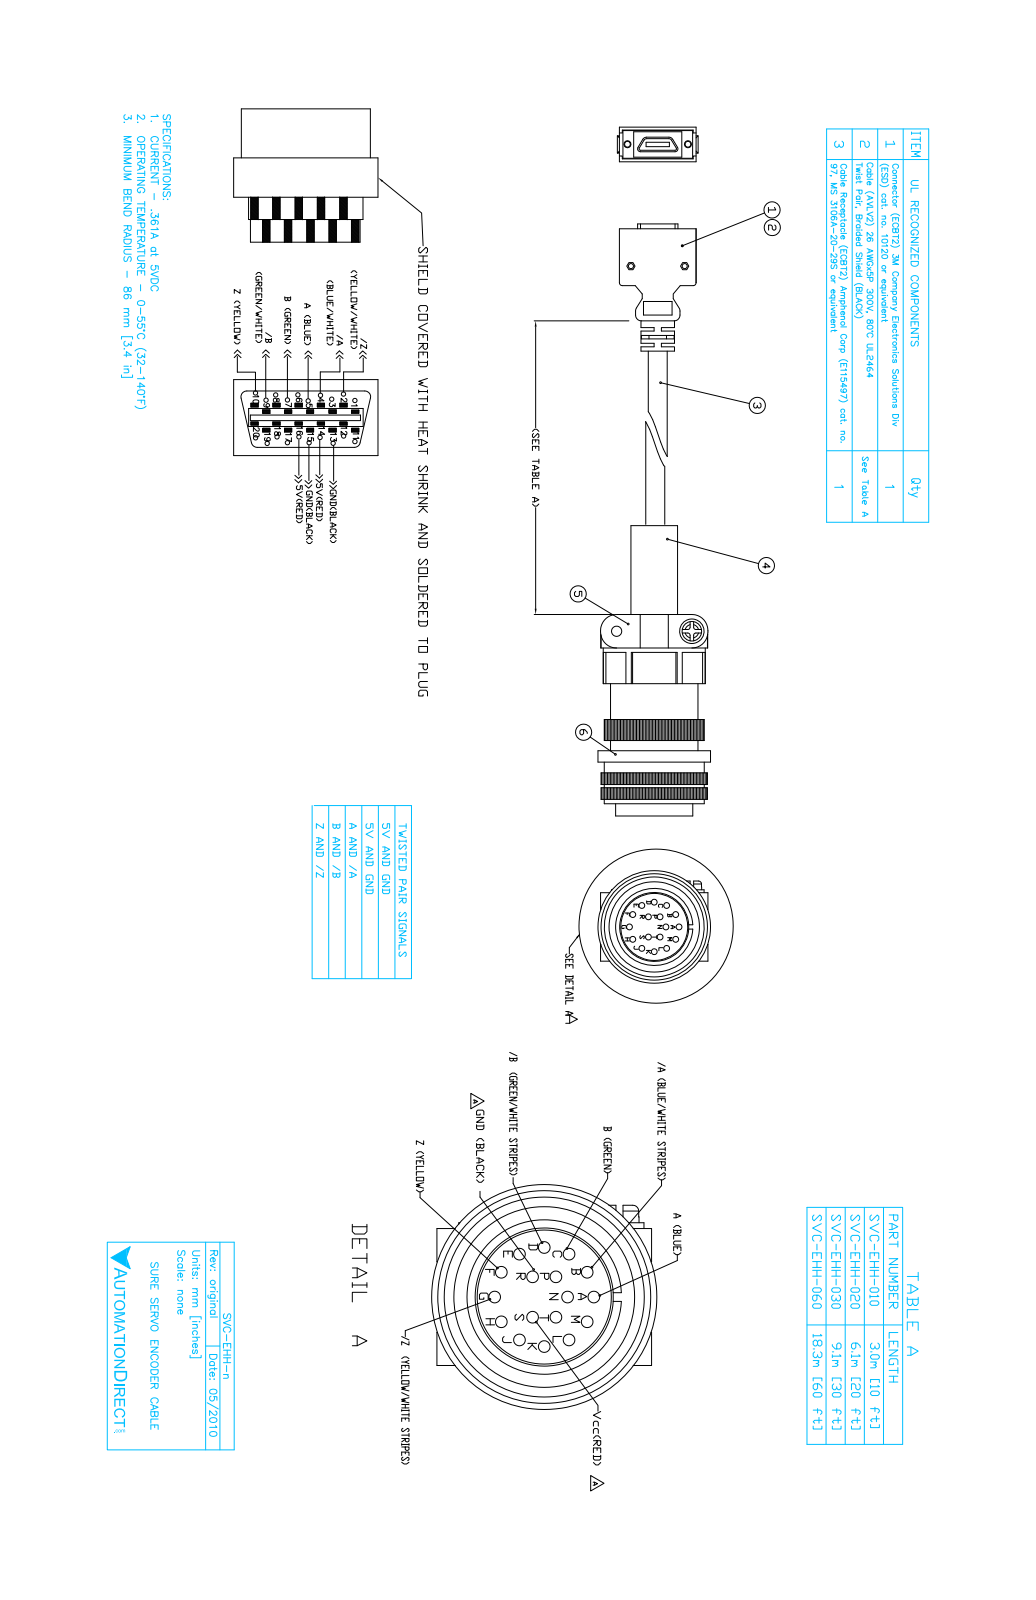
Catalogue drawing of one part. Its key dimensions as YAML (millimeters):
part_name: "SVC-EHH-060"
step_written_by: "SolidWorks 2015 (AUTOMOTIVE_DESIGN)"
units: millimeters
bodies: {solids: 8, faces: 739, planar: 411, cylindrical: 210, other: 118}
overall_size: [170.5, 68.84, 37.12]
volume: 58565
surface_area: 32593
round_holes:
  - {diameter: 2, count: 17}
  - {diameter: 4, count: 2}
  - {diameter: 9, count: 1}
  - {diameter: 16, count: 1}
  - {diameter: 23.4, count: 1}
  - {diameter: 29.8, count: 1}
  - {diameter: 32.5, count: 1}
round_bosses_or_shafts:
  - {diameter: 6.5, count: 2}
  - {diameter: 37.12, count: 1}
  - {diameter: 35.3, count: 1}
  - {diameter: 34.8, count: 1}
  - {diameter: 34.7, count: 1}
  - {diameter: 33.3, count: 1}
  - {diameter: 29.9, count: 1}
  - {diameter: 26.2, count: 1}
partial_cylinders:
  - {radius: 6.5, count: 2}
  - {radius: 9.88, count: 1}
  - {radius: 17.81, count: 1}
face_to_face_distances: [45.23, 6.7, 10.7, 39.13, 6.1, 2.5, 1.01, 38.12, 44.22, 1.49]
hole_center_spacings: [8.75, 4.53, 12.37, 15.16, 16.91, 4.25, 4.52, 12.38]
